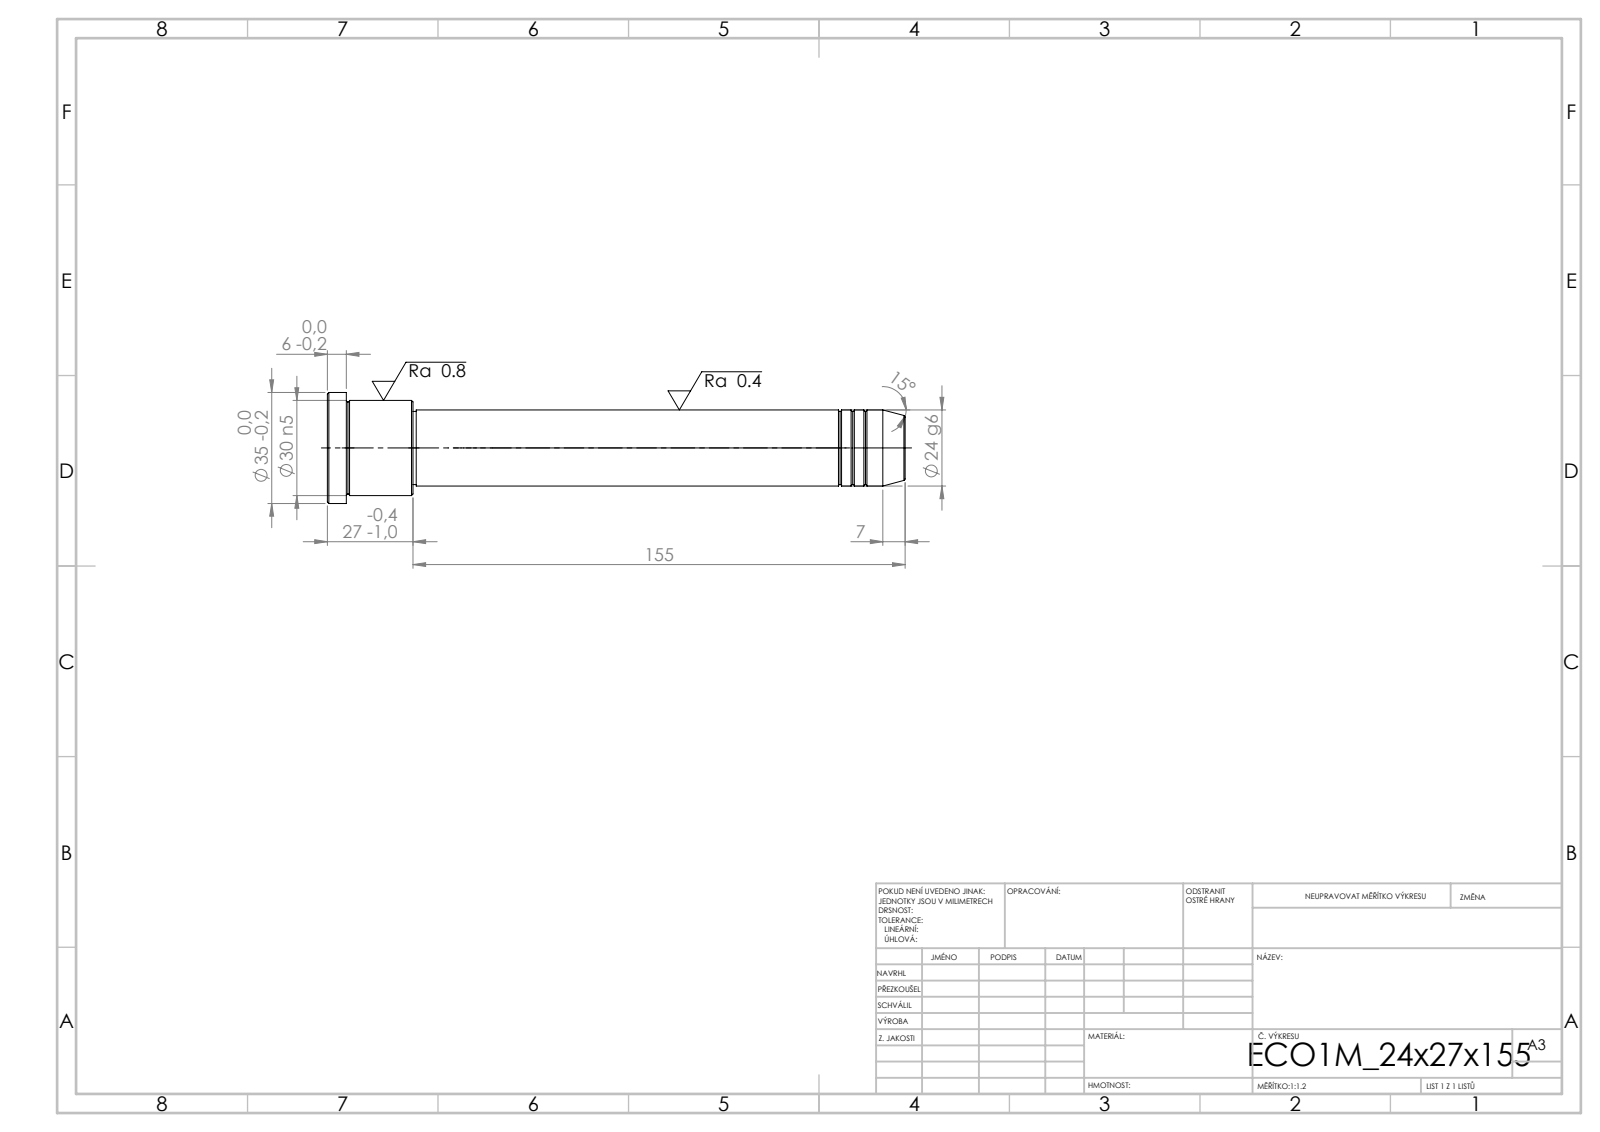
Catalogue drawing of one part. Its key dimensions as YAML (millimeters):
step_written_by: "SolidWorks 2019 (CONFIG_CONTROL_DESIGN)"
units: millimeters
bodies: {solids: 1, faces: 43, planar: 5, cylindrical: 14, other: 24}
overall_size: [182, 35, 35]
volume: 90080
surface_area: 16269
round_bosses_or_shafts:
  - {diameter: 35, count: 1}
  - {diameter: 30, count: 1}
  - {diameter: 24, count: 1}
  - {diameter: 23, count: 1}
face_to_face_distances: [182, 176, 6, 155, 21, 27, 154, 1, 22, 28]
